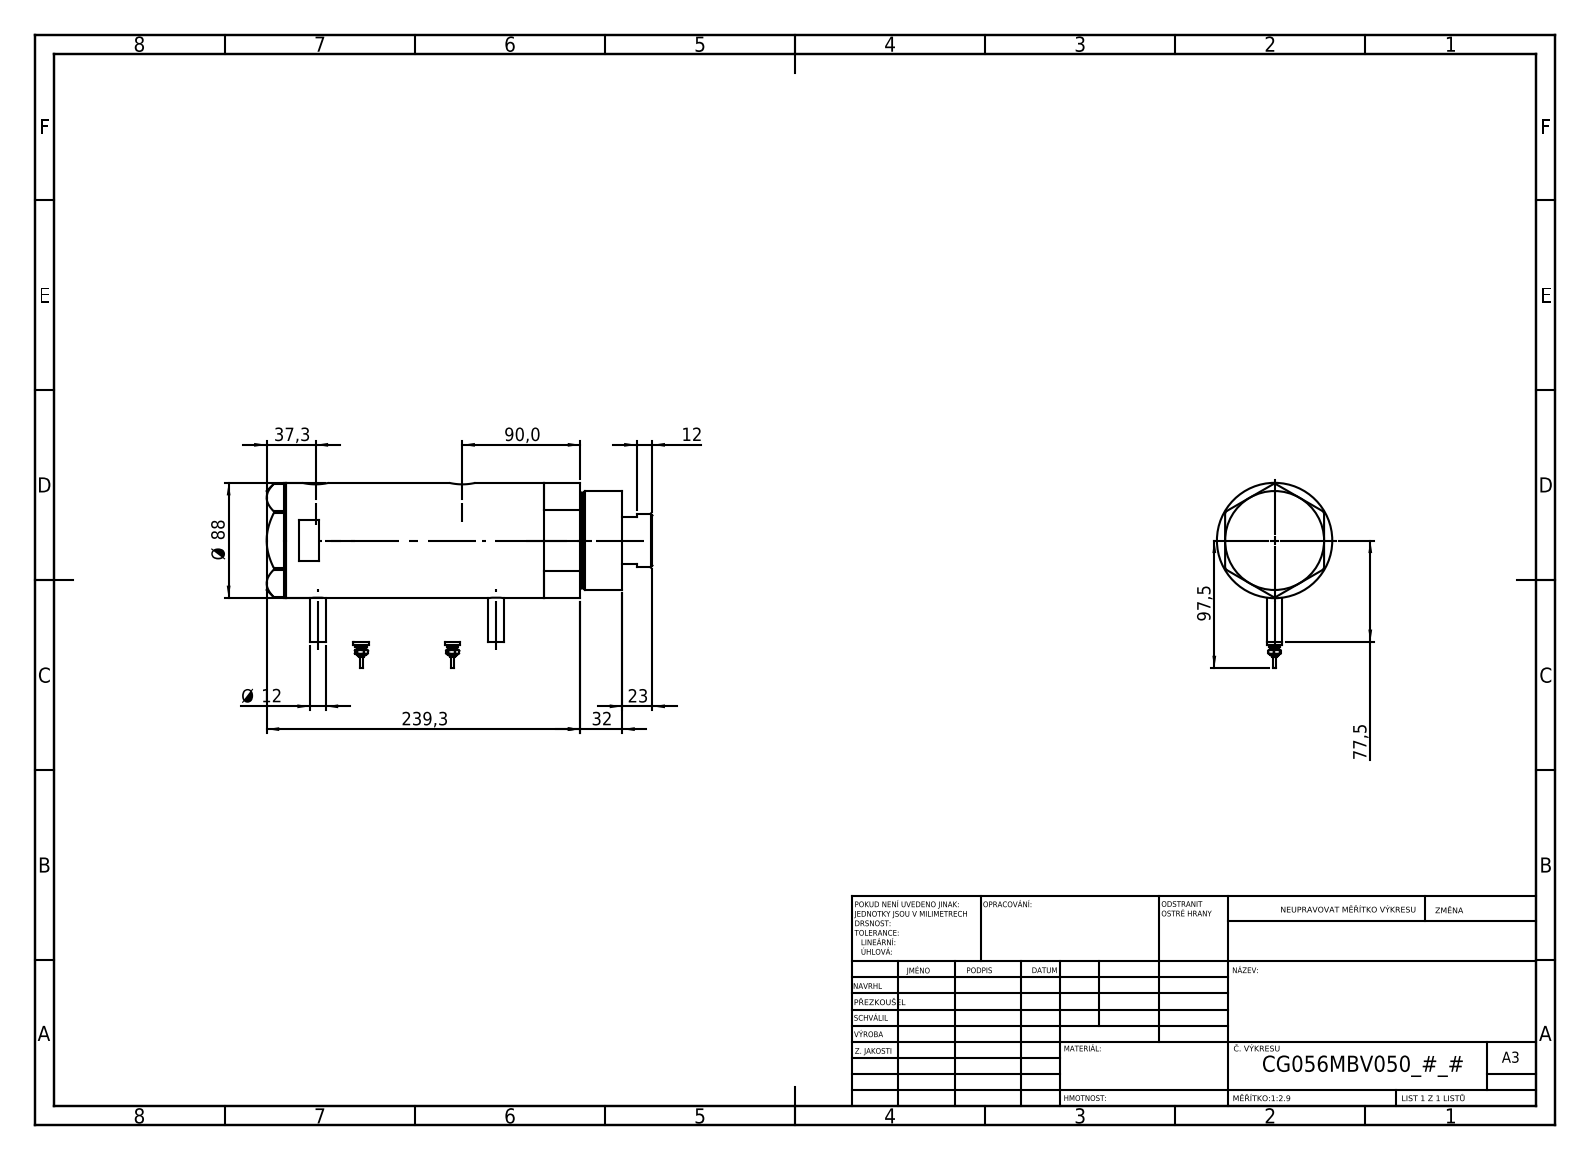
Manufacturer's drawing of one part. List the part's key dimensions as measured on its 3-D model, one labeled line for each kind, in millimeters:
Part name (STEP PRODUCT): V270CG_MIDDLE; V270CG_FRONT; V270CG_VC; V270CG_BACK (+1 more)
STEP written by: SolidWorks 2019 (CONFIG_CONTROL_DESIGN)
Units: millimetres
Bodies: 6 solids, 213 faces (80 planar, 69 cylindrical, 64 other)
Overall size (bounding box): 294.3 × 141.5 × 88
Volume: 1 541 000 mm³ · Surface area: 224 589 mm²
Round holes (diameter × count): ⌀12.5 ×2, ⌀13.16 ×2, ⌀20 ×2, ⌀14.5 ×1, ⌀42 ×1, ⌀43.5 ×1, ⌀56 ×1, ⌀60 ×1, ⌀80 ×1
Round bosses / shafts (diameter × count): ⌀12 ×4, ⌀9 ×2, ⌀7 ×2, ⌀4.5 ×2, ⌀2.5 ×2, ⌀88 ×1, ⌀75 ×1, ⌀73 ×1
Main face-to-face distances: 134.4, 26, 108.4, 15, 41, 149.4, 256.3, 271.3, 230.3, 121.9
Hole centre spacings: 1.7, 25.8, 110.3, 112, 136.1, 137.8
